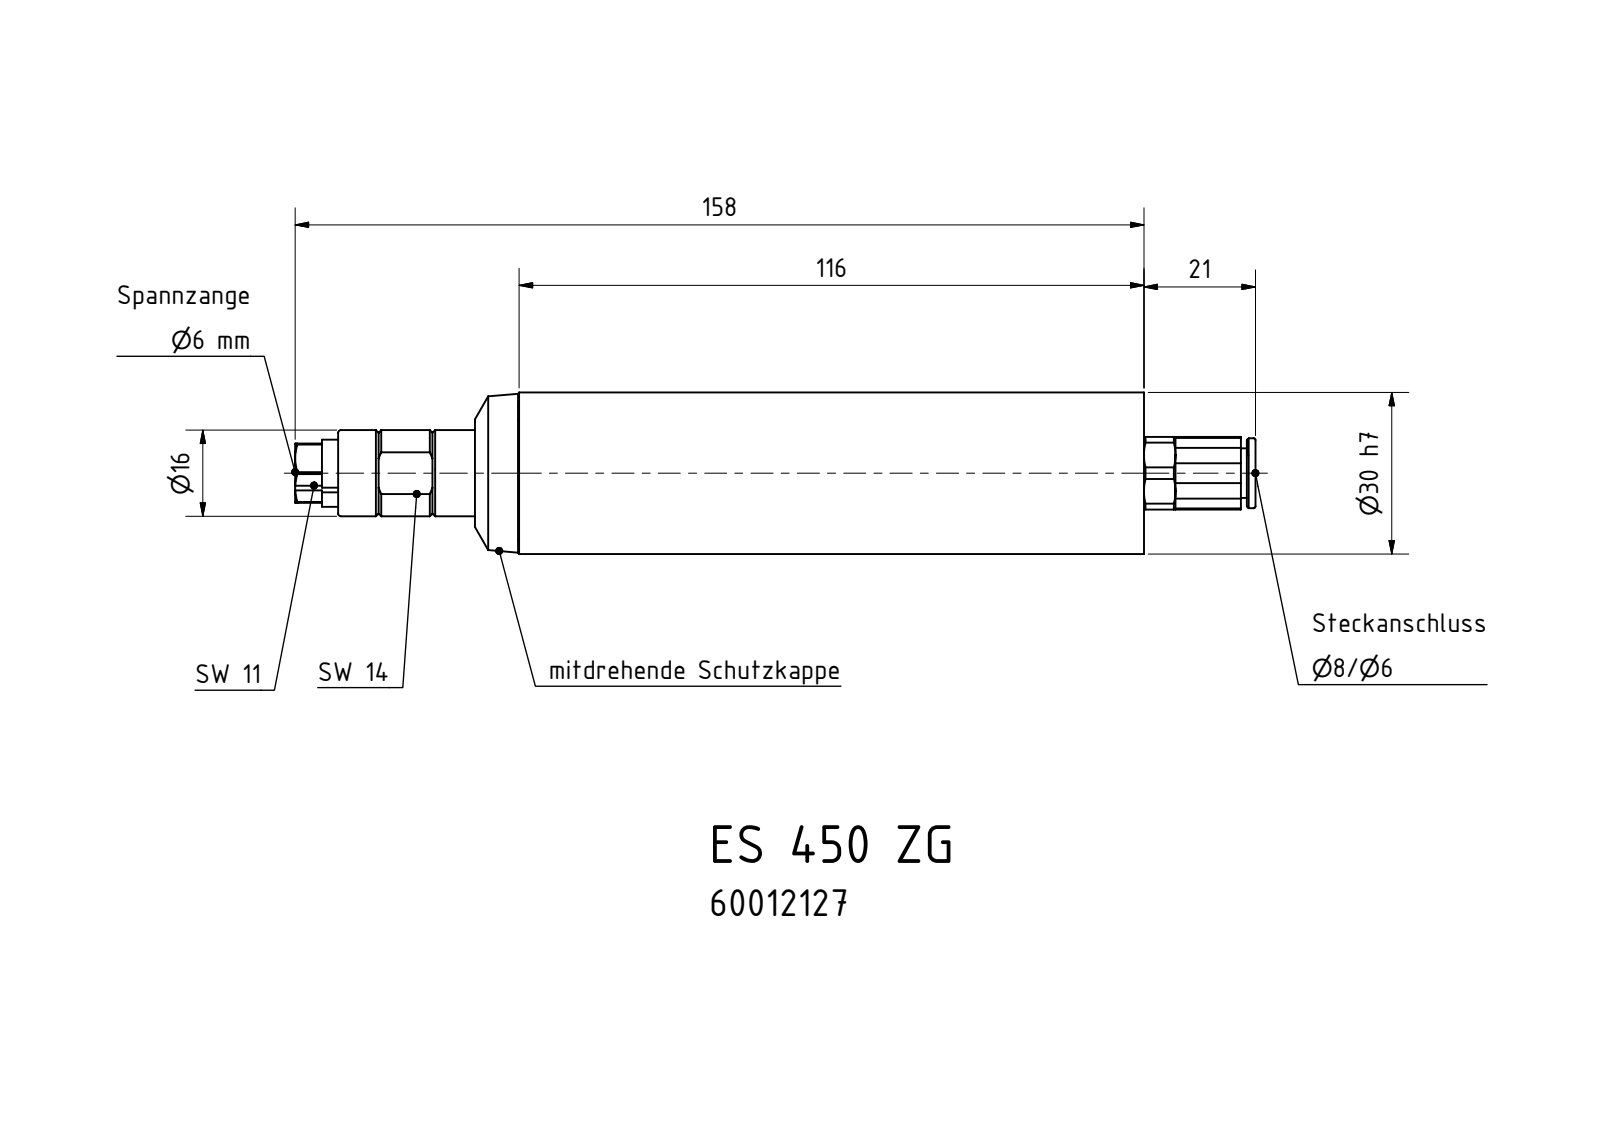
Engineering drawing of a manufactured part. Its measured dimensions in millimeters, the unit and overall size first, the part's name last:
Units: millimetres
Overall size (bounding box): 178.3 × 30 × 30
Round holes (diameter × count): ⌀8 ×1, ⌀9.18 ×1
Round bosses / shafts (diameter × count): ⌀30 ×1, ⌀27.2 ×1, ⌀16 ×1, ⌀13 ×1, ⌀12.5 ×1, ⌀9.2 ×1
Partial cylindrical surfaces — rounded edges, fillets, slot ends (radius × count): R50 ×3, R3.68 ×1, R6.75 ×1, R7.25 ×1
Main face-to-face distances: 13.5, 6, 7, 1.25, 12.25, 8, 116, 3, 8.2, 124.2
Volume: 93 046 mm³ · Surface area: 17 275 mm²
Bodies: 1 solid, 150 faces (73 planar, 31 cylindrical, 46 other)
Part name (STEP PRODUCT): ES 450 ZG_60012127
STEP written by: Autodesk Inventor 2008 (AUTOMOTIVE_DESIGN)
